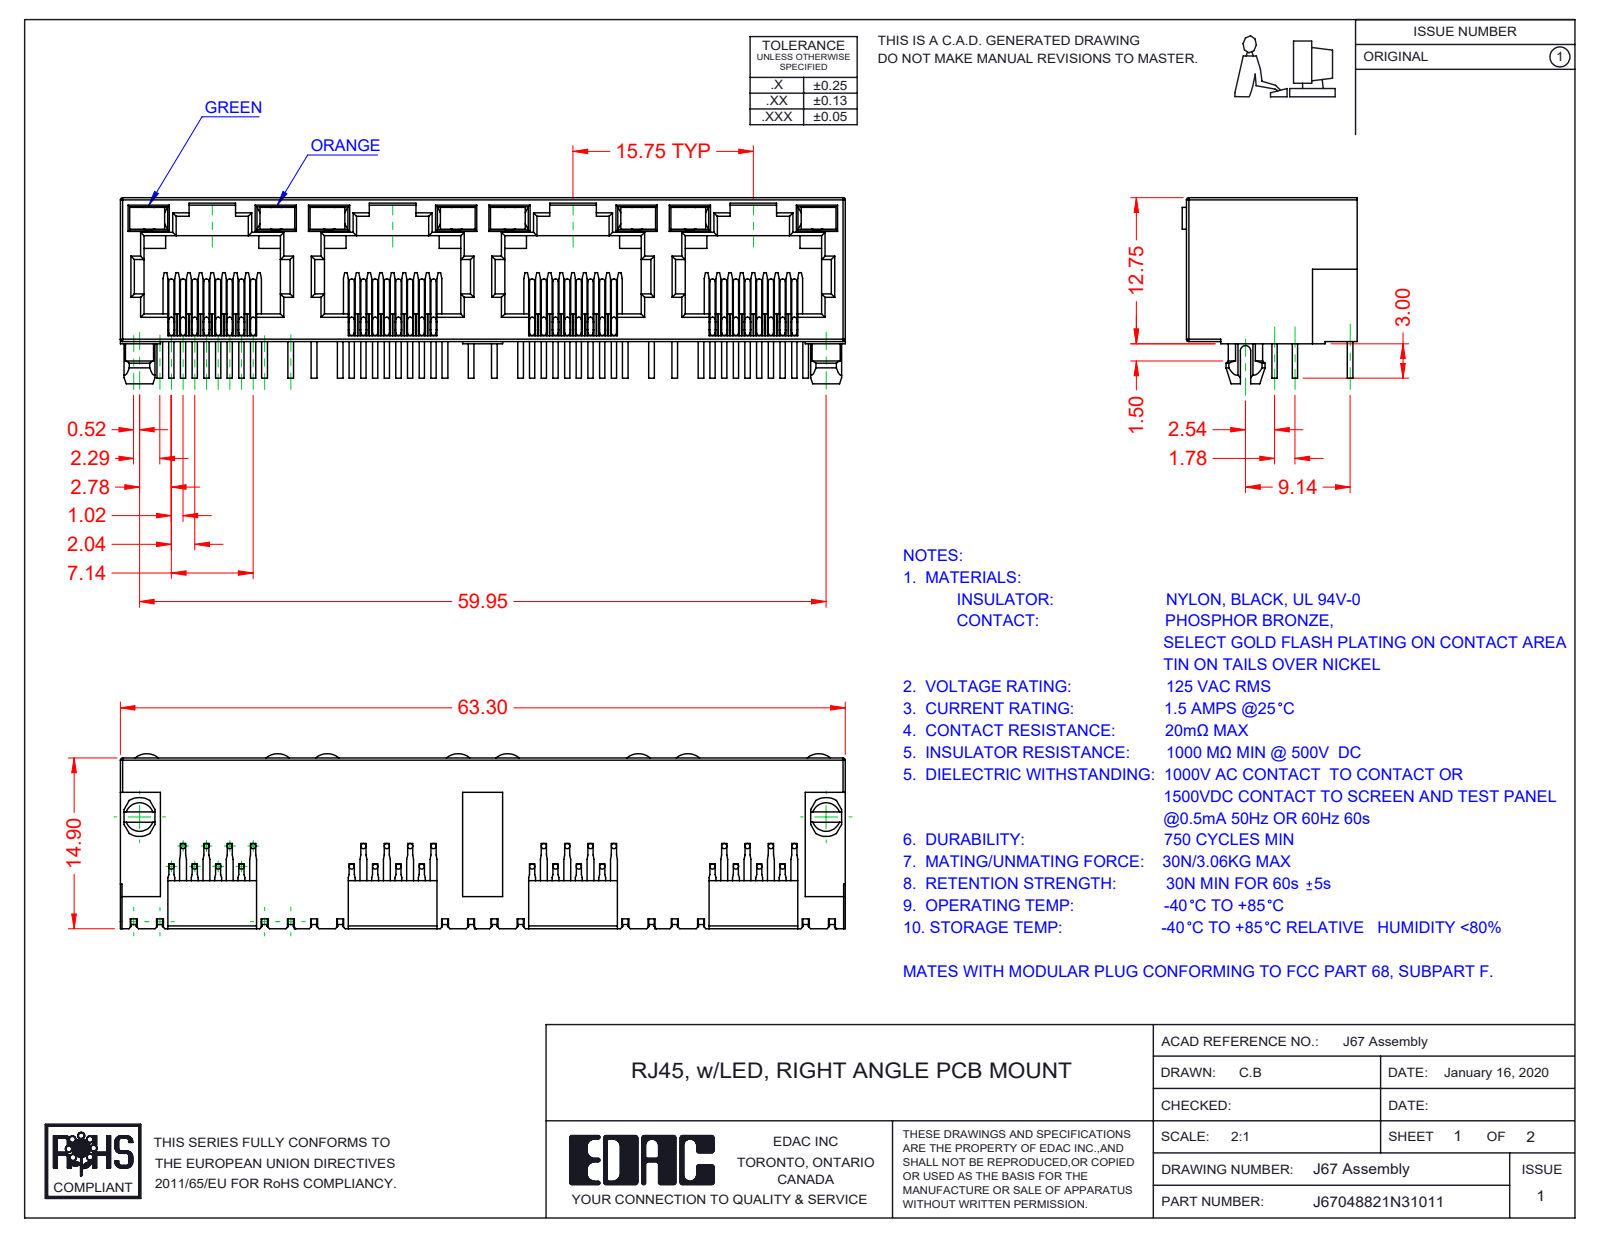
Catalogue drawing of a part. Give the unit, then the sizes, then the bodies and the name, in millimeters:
Units: millimetres
Overall size (bounding box): 63.3 × 16.25 × 15.28
Round bosses / shafts (diameter × count): ⌀0.46 ×96
Partial cylindrical surfaces — rounded edges, fillets, slot ends (radius × count): R0.2 ×66, R0.3 ×29, R0.45 ×9, R1.55 ×8, R1.5 ×2, R1.7 ×2, R0.35 ×1, R1 ×1
Main face-to-face distances: 0.5, 12.55, 1.89, 0.89, 10, 15.75, 1, 1.39, 11, 11.89
Volume: 5 159 mm³ · Surface area: 11 573 mm²
Bodies: 41 solids, 2465 faces (1781 planar, 476 cylindrical, 208 other)
Part name (STEP PRODUCT): 67 LED RH_4-Orange; 67 LED LH_3-Green; 67 Contacts; 67 Insulator (+1 more)
STEP written by: SolidWorks 2016 (CONFIG_CONTROL_DESIGN)
